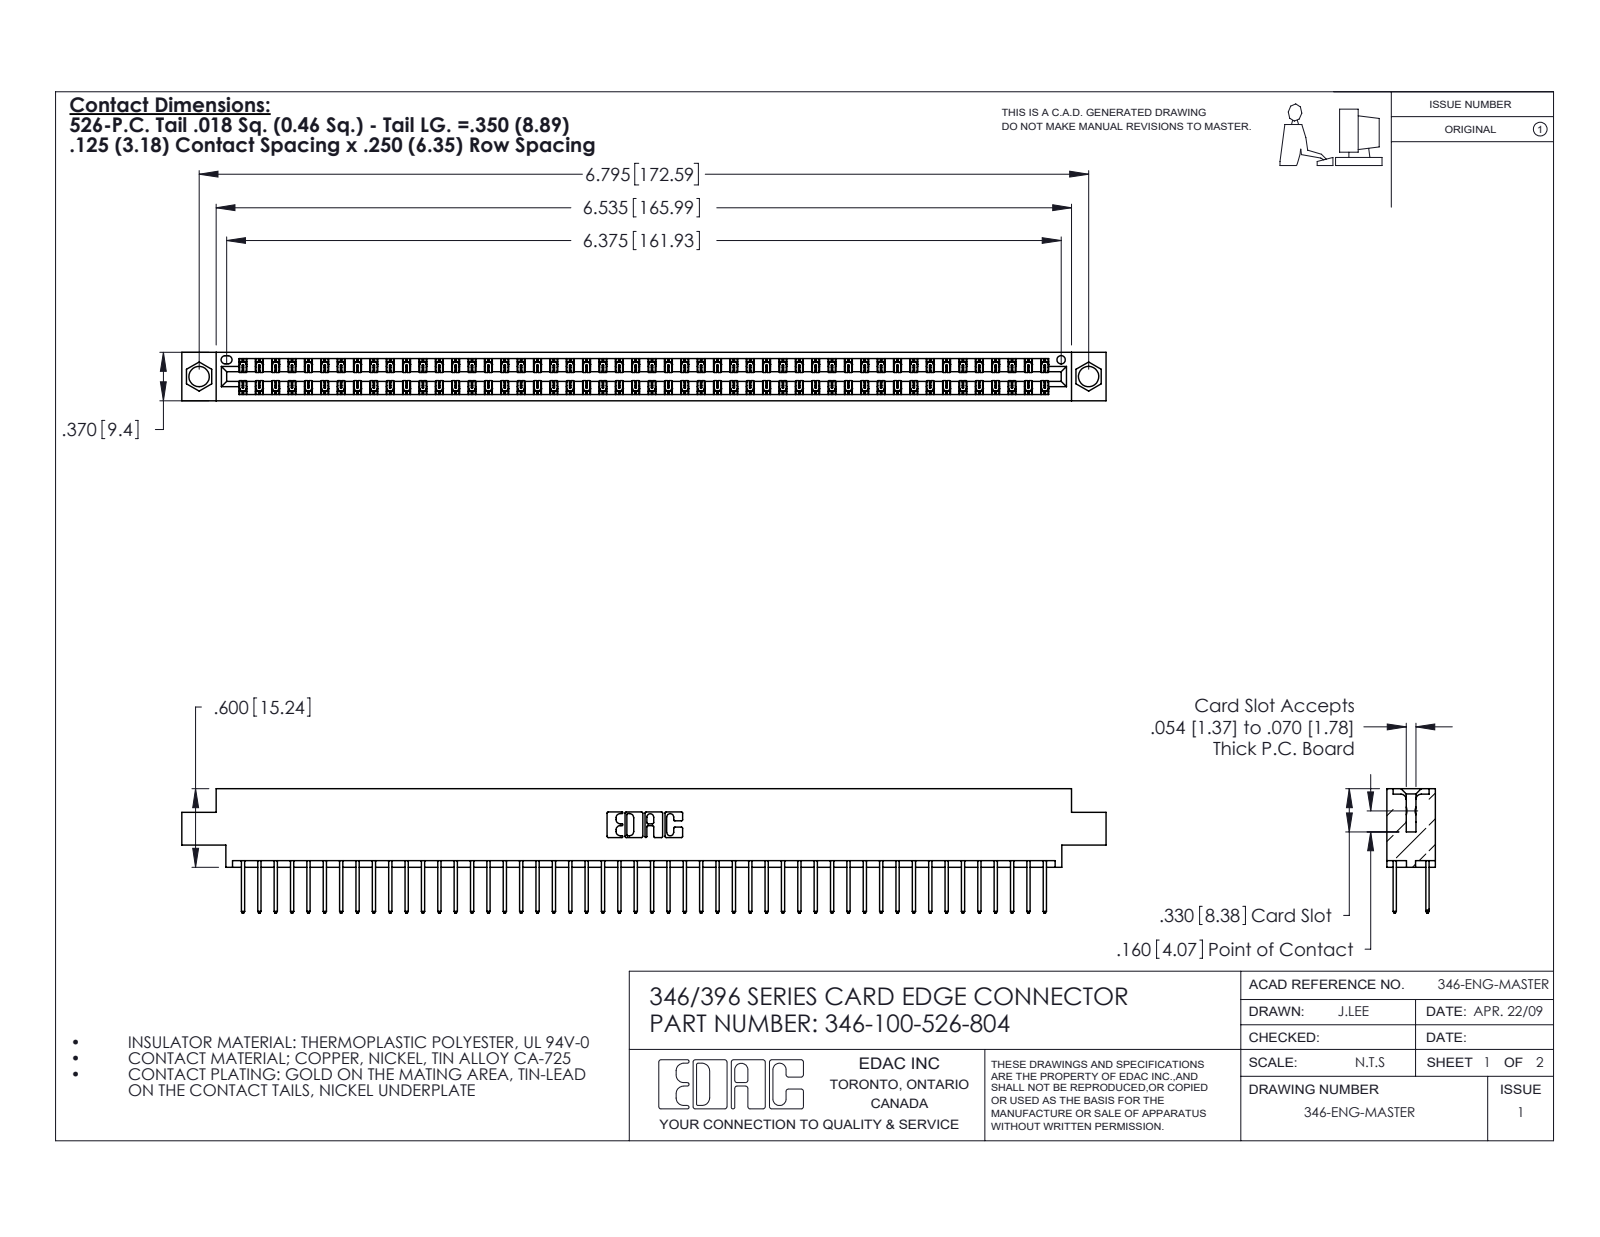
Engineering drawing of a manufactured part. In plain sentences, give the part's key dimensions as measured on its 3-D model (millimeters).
The part is named "345-292-001_345-293-126; 346-100-526-804; 346 Part_0.170 Offset - 0.156 Dia-TH". Its 3-D file was written by "SolidWorks 2020 (CONFIG_CONTROL_DESIGN)". It is 101 solids with 5340 faces: 3594 planar, 1746 cylindrical and 0 other. Overall it measures 179.3 by 24.1 by 9.4 millimeters. Its volume is 17 450 cubic millimeters and its surface area 24 880 square millimeters. Round holes: 2 of diameter 4, 1 of diameter 1.6. Partial cylindrical surfaces (rounded edges, fillets, slot ends): 150 of radius 0.2, 100 of radius 0.3, 22 of radius 0.3, 6 of radius 0.2, 6 of radius 0.8, 3 of radius 0.7, 2 of radius 0.4, 2 of radius 0.6. The main face-to-face distances are 1.2, 8.2, 6.4, 9.4, 1.8, 7.6, 0.6, 7, 5.6, 3.8. The hole center spacings are 6.2, 167.3, 172.6.
